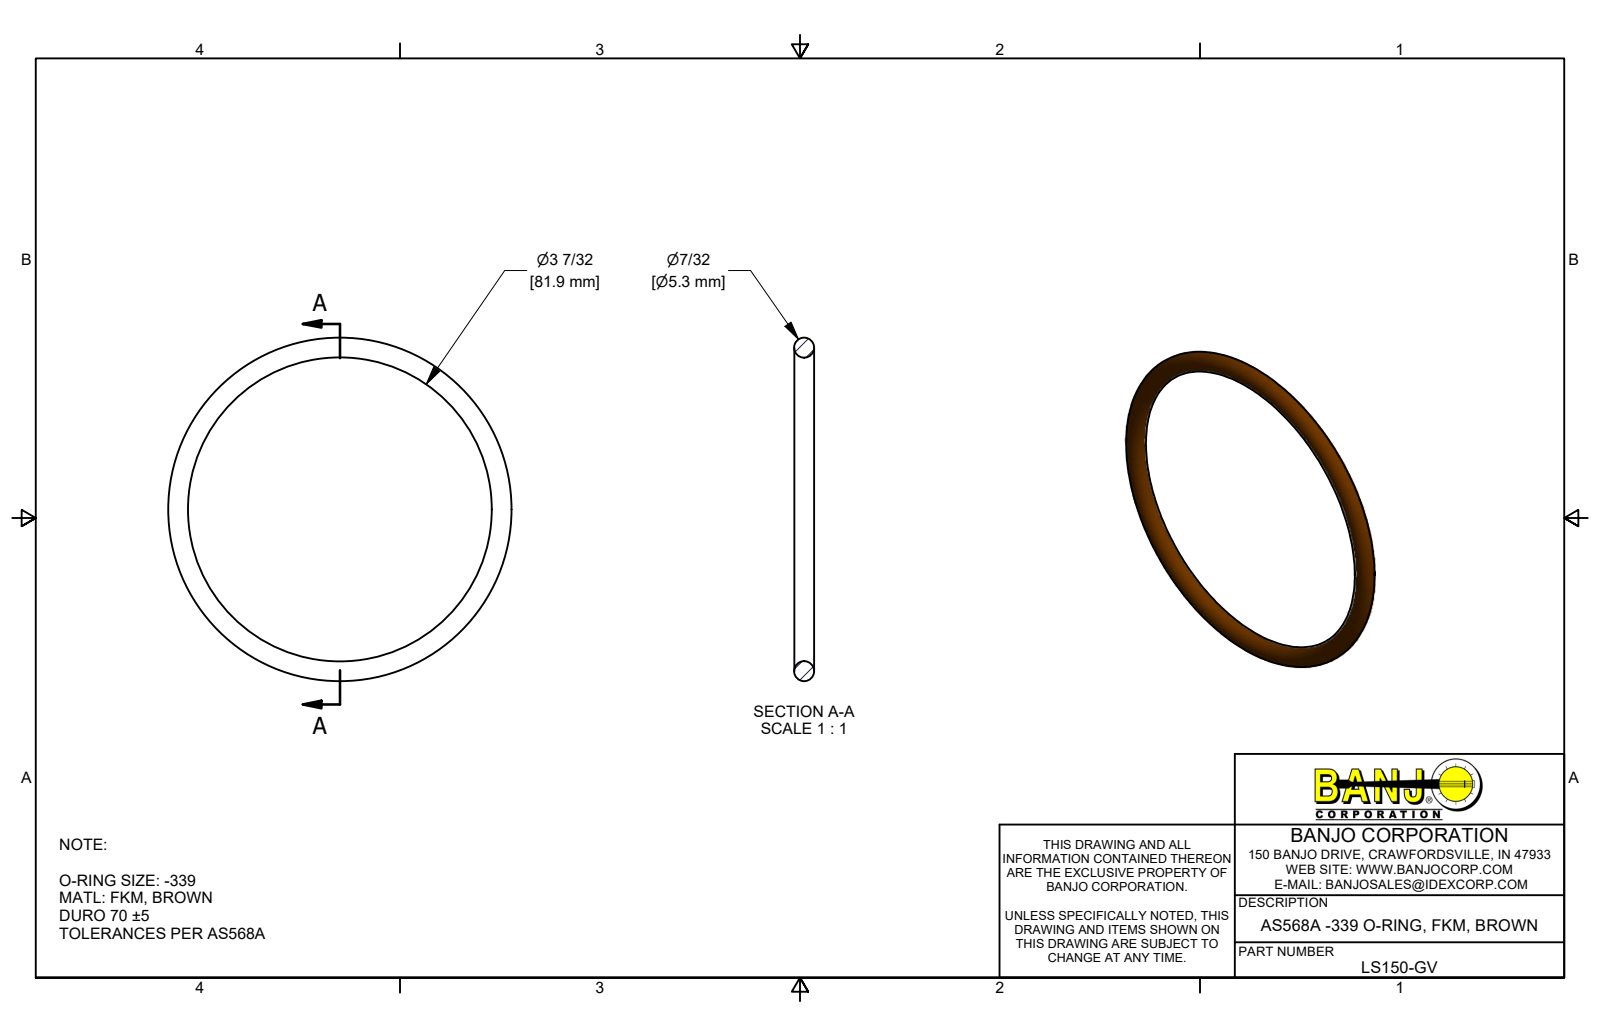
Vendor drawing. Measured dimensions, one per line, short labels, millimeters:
name: LS150-GV
written by: Autodesk Inventor 2019 (AUTOMOTIVE_DESIGN)
unit: mm
bodies: 1 solid, 1 faces (0 planar, 0 cylindrical, 1 other)
size: 92.6 × 92.6 × 5.3
volume: 6 130 mm³; area: 4 593 mm²
